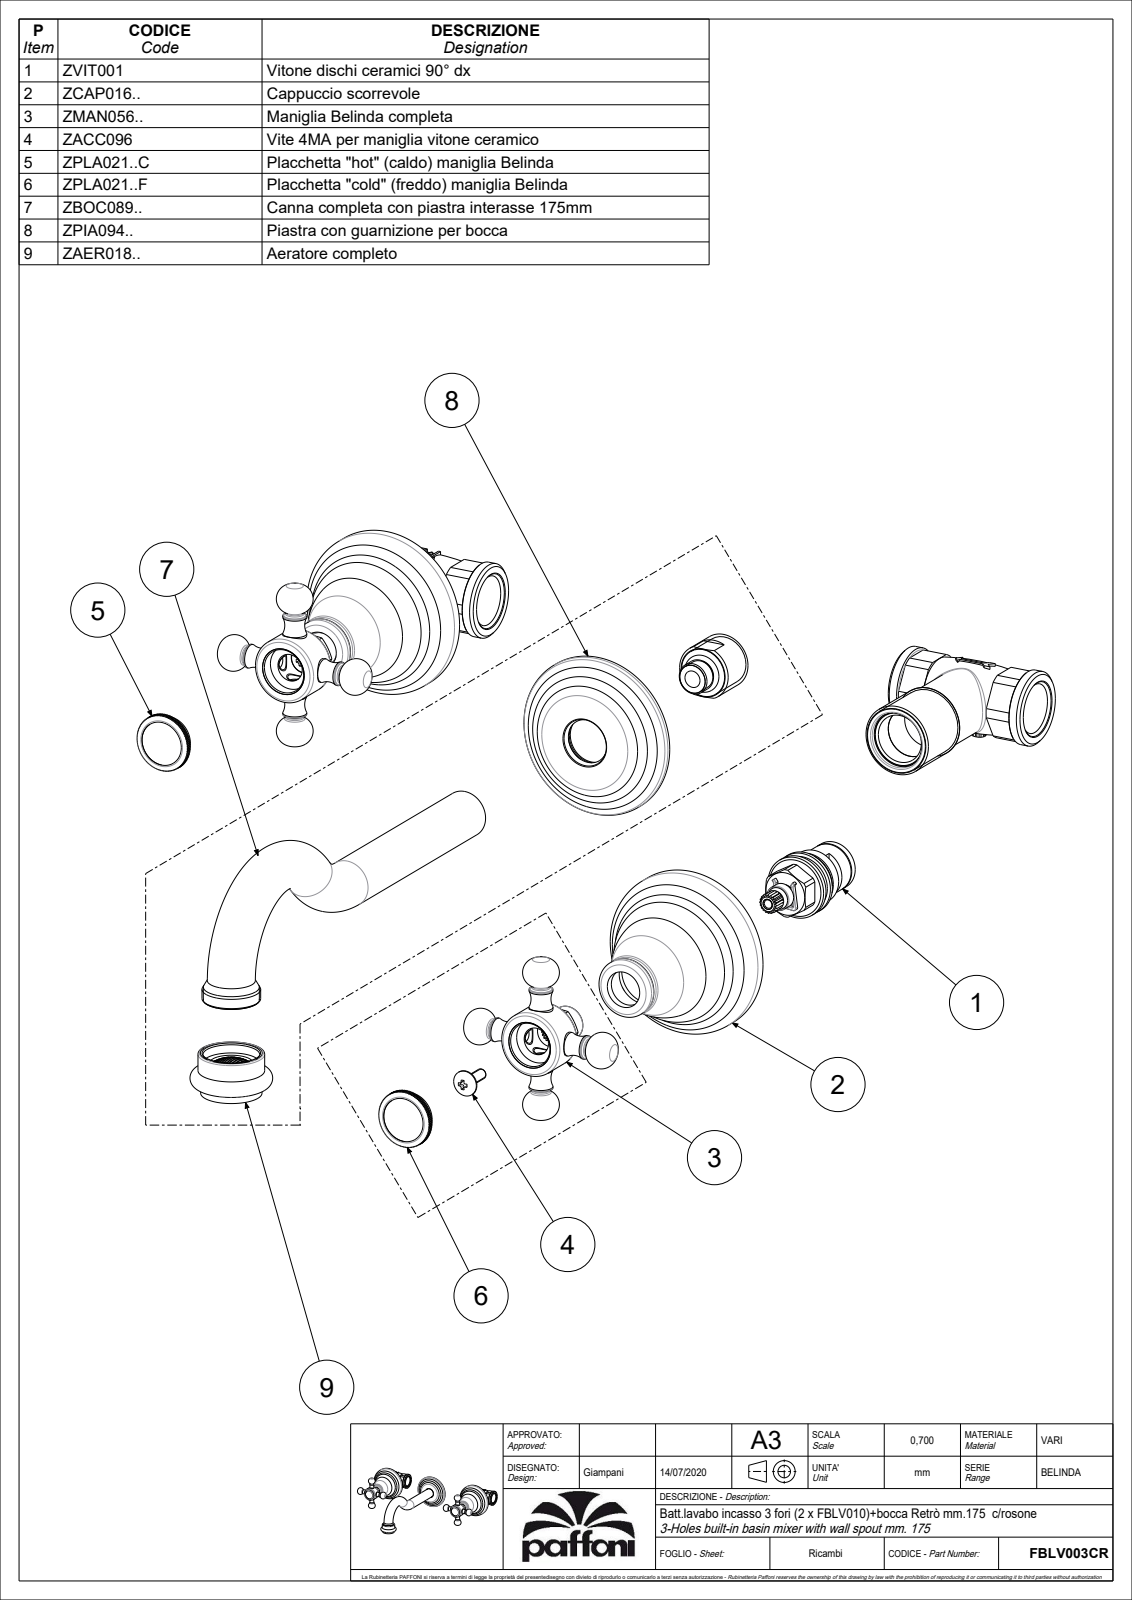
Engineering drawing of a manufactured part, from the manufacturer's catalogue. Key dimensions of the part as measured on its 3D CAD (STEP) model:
Part name (STEP PRODUCT): FBLV003CR
STEP written by: CREO PARAMETRIC BY PTC INC, 2020044 (CONFIG_CONTROL_DESIGN)
Units: millimetres
Bodies: 3 solids, 917 faces (439 planar, 282 cylindrical, 196 other)
Overall size (bounding box): 264.07 × 190.5 × 64.07
Volume: 253 290 mm³ · Surface area: 51 872 mm²
Round bosses / shafts (diameter × count): ⌀25 ×3, ⌀9 ×3, ⌀7 ×3, ⌀63 ×2, ⌀22.5 ×2, ⌀14 ×2, ⌀13 ×2, ⌀62 ×1
Partial cylindrical surfaces — rounded edges, fillets, slot ends (radius × count): R11 ×2
Main face-to-face distances: 10, 63.5, 53.5, 50, 40, 13.5, 15, 15.2, 173.2, 4
